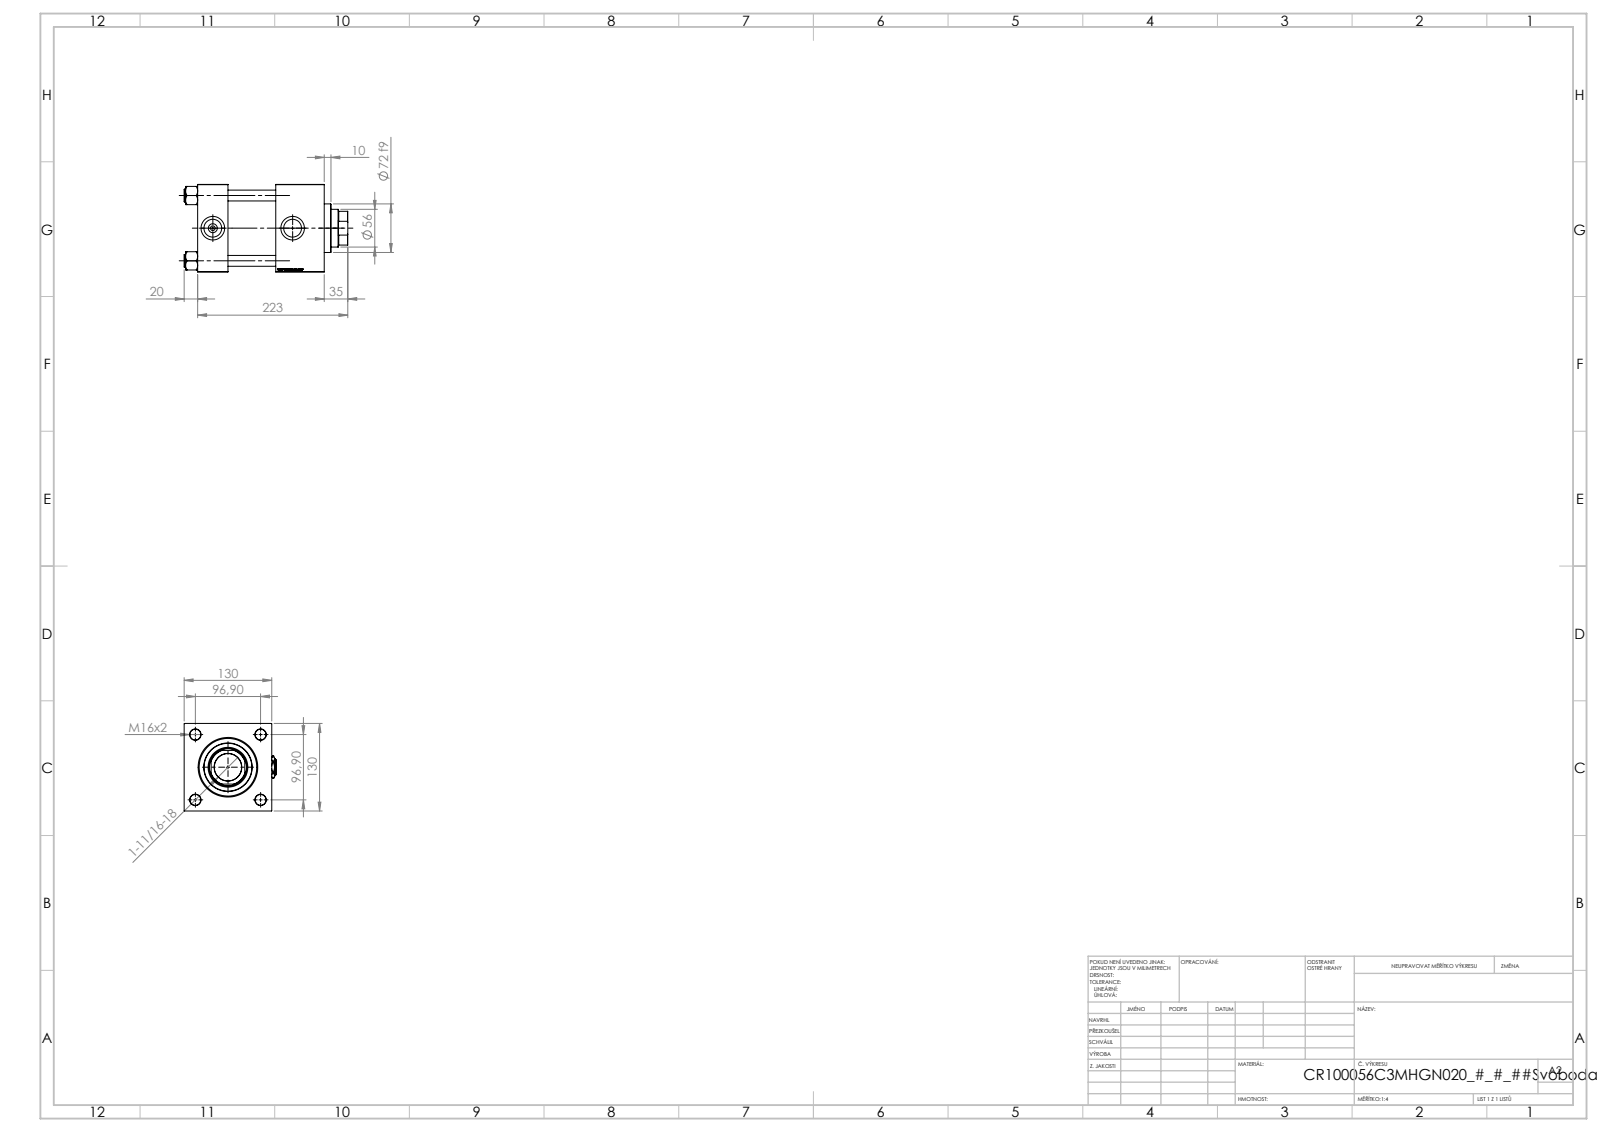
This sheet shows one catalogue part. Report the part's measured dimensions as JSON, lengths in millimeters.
{"part_name": "V215CR_C_Body; NUT_M5_C; V215_VC_A; V215CR_C_TYCINKA (+2 more)", "step_written_by": "SolidWorks 2019 (CONFIG_CONTROL_DESIGN)", "units": "millimeters", "bodies": {"solids": 13, "faces": 1297, "planar": 621, "cylindrical": 98, "other": 578}, "overall_size": [243, 137, 130], "volume_mm3": 2461000, "surface_area_mm2": 340431, "round_holes": [[16, 4], [7, 2], [26.44, 2], [35, 2], [40.5, 1], [56, 1], [59, 1], [76, 1], [85.5, 1], [100, 1]], "round_bosses_or_shafts": [[19, 4], [106, 1], [72, 1]], "partial_cylinders_radius": [[27, 1]], "face_to_face_distances": [130, 45, 188, 143, 116, 71, 72, 20, 51, 92], "hole_center_spacings": [68.52, 96.9, 137.04, 118.5]}
